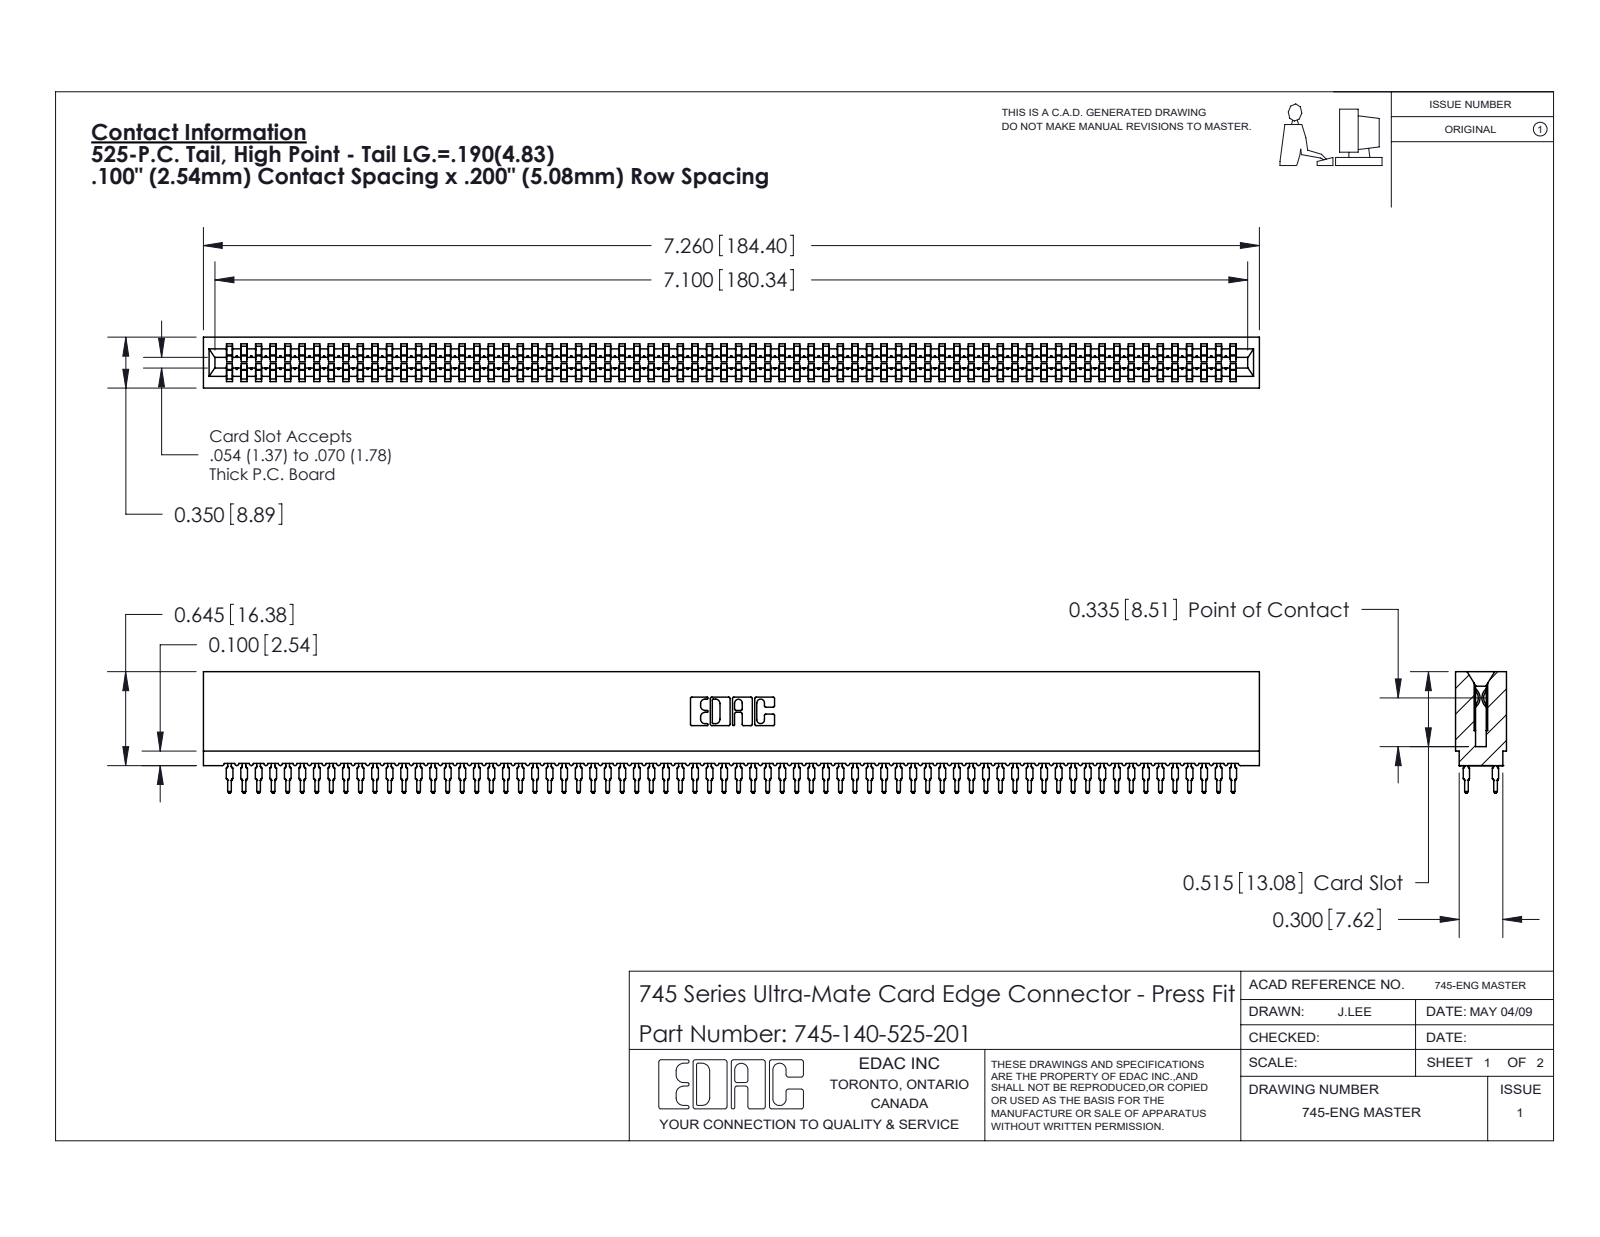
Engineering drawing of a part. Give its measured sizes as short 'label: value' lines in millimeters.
name: 745-140-525-201; 745 Part_Insulator Option - 01; 745-292-001_525
written by: SolidWorks 2020 (CONFIG_CONTROL_DESIGN)
unit: mm
bodies: 141 solids, 12625 faces (6495 planar, 2490 cylindrical, 3640 other)
size: 184.4 × 21.2 × 8.9
volume: 16 400 mm³; area: 33 860 mm²
rounds: 280× R0.5, 140× R0.4, 22× R0.3, 8× R0.1, 8× R0.3, 6× R0.2, 6× R0.8, 3× R0.7
face distances: 8.9, 1.6, 7.3, 1.1, 7.7, 0.5, 6.2, 3.5, 5.4, 2.4
